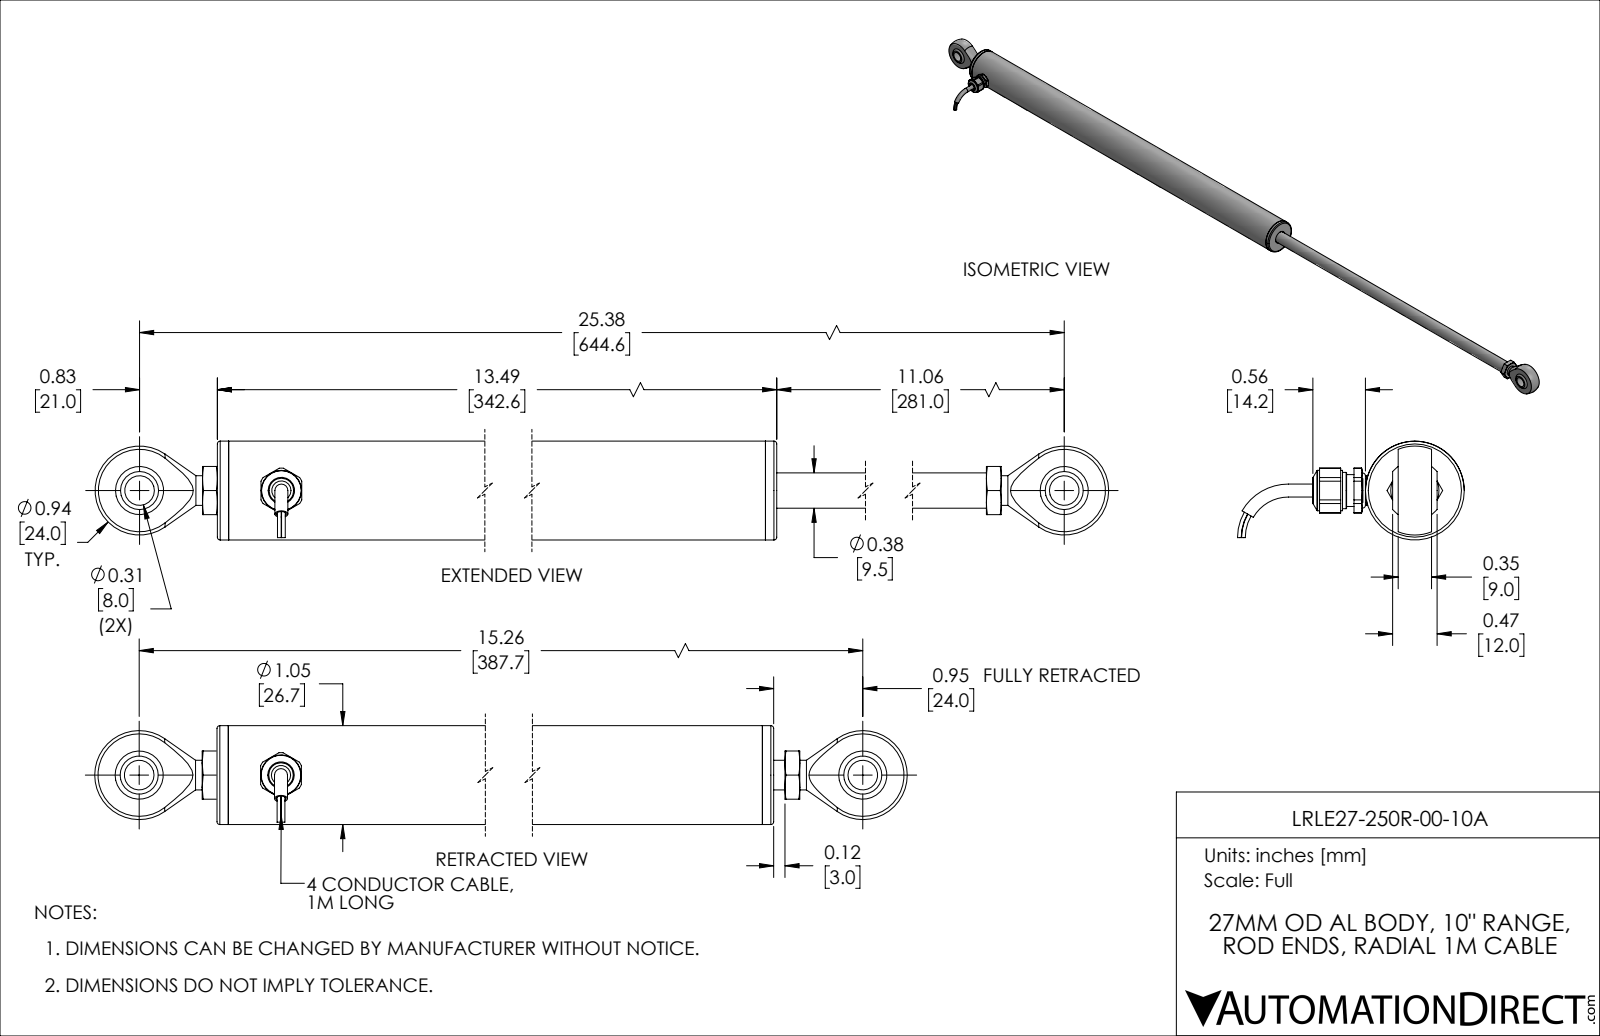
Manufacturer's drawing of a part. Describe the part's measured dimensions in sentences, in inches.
The part is named "LRLE27-250R-00-10A_Retracted". Its 3-D file was written by "SolidWorks 2019 (AUTOMOTIVE_DESIGN)". It is 28 solids with 298 faces: 114 planar, 92 cylindrical and 92 other. Overall it measures 16.088 by 2.409 by 1.05 inches. Its volume is 7.237 cubic inches and its surface area 147.2 square inches. Round holes: 2 of diameter 0.268, 2 of diameter 0.315, 1 of diameter 0.106, 1 of diameter 0.138, 1 of diameter 0.156, 1 of diameter 0.187, 1 of diameter 0.201, 1 of diameter 0.205, 1 of diameter 0.272, 1 of diameter 0.275, 1 of diameter 0.313, 1 of diameter 0.36. Round bosses or shafts: 4 of diameter 0.039, 2 of diameter 0.315, 1 of diameter 1.05, 1 of diameter 0.85, 1 of diameter 0.848, 1 of diameter 0.685, 1 of diameter 0.625, 1 of diameter 0.5. Partial cylindrical surfaces (rounded edges, fillets, slot ends): 2 of radius 0.01, 2 of radius 0.067, 2 of radius 0.25, 1 of radius 0.197, 1 of radius 0.224, 1 of radius 0.238, 1 of radius 0.344, 1 of radius 0.407. The main face-to-face distances are 0.354, 13.49, 0.737, 12.753, 0.12, 13.37, 0.5, 1.65, 0.913, 11.84. The hole center spacings are 1.507, 13.637, 15.144.
